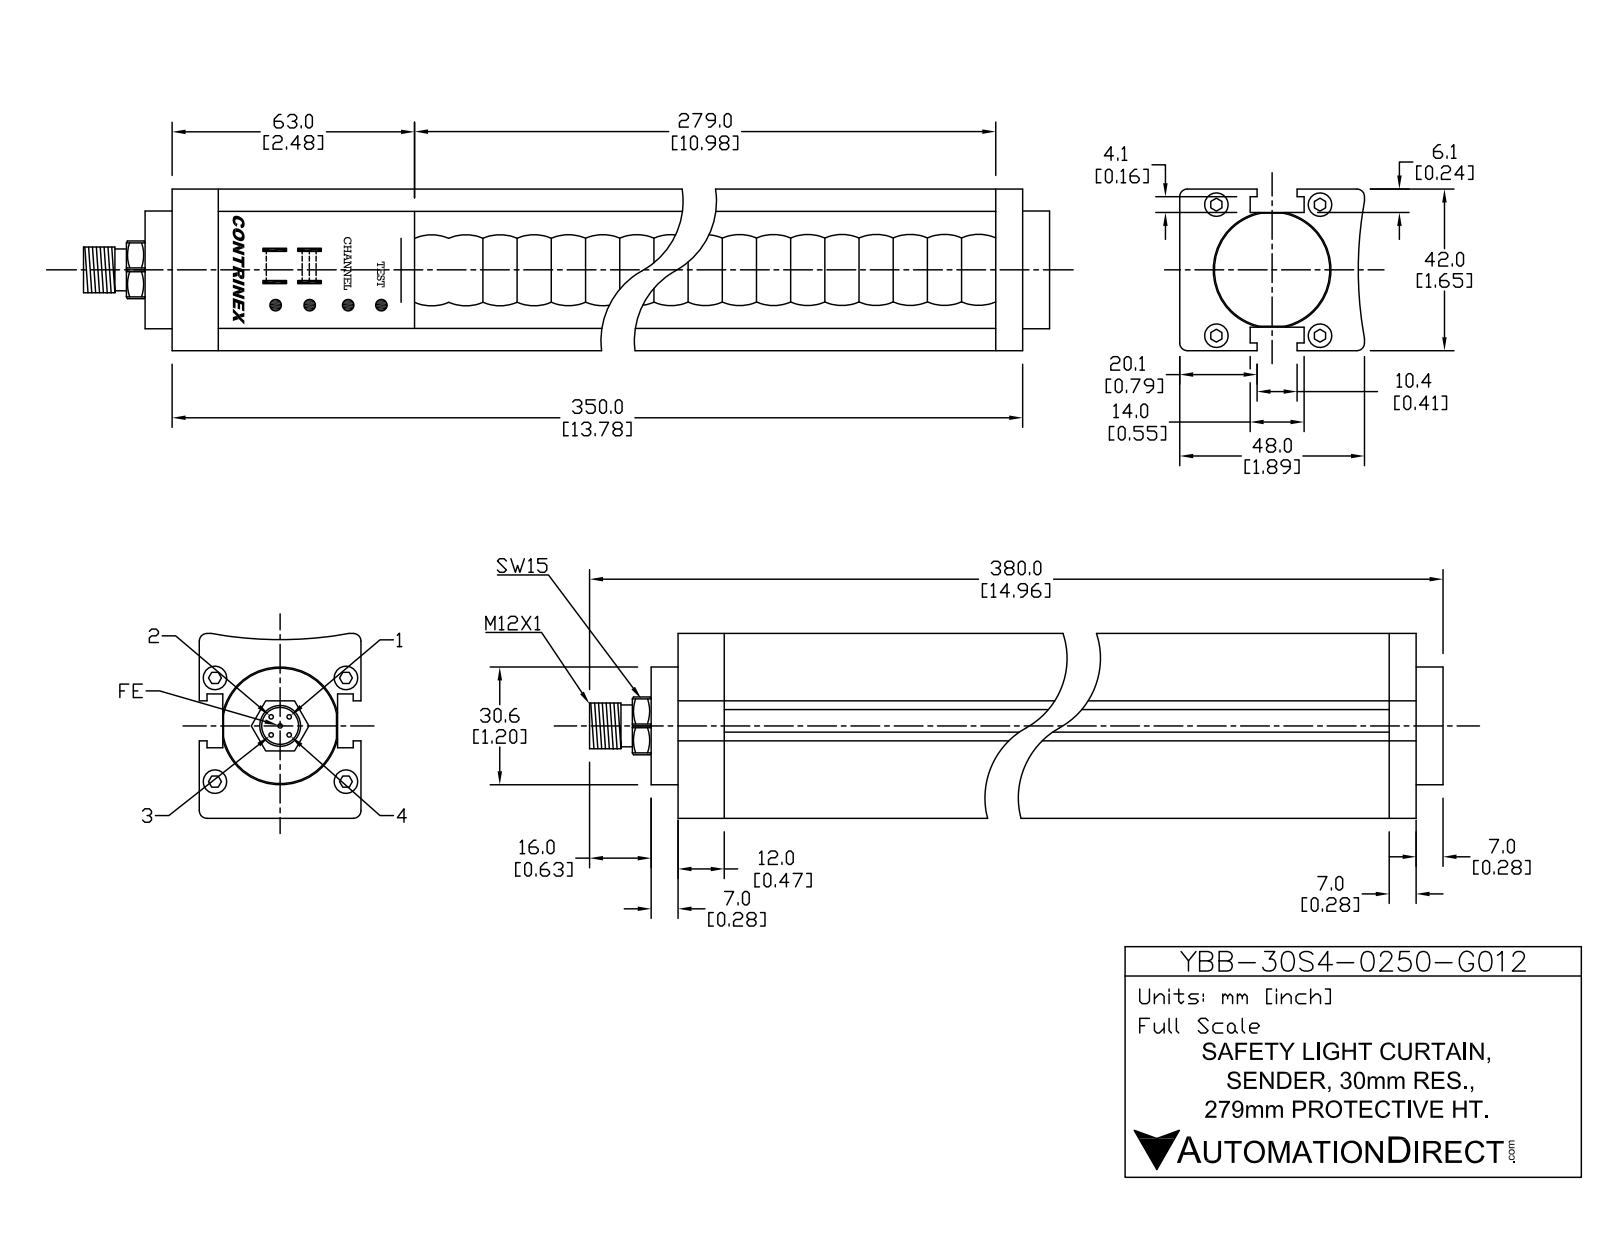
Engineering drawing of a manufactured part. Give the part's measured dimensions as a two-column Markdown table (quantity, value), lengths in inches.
| quantity | value |
| --- | --- |
| part name | YBB-30S4-0250-G012 |
| STEP written by | SolidWorks 2016 (AUTOMOTIVE_DESIGN) |
| units | inches |
| bodies | 19 solids, 440 faces (208 planar, 168 cylindrical, 64 other) |
| overall size | 14.961 × 1.89 × 1.654 |
| volume | 38.88 in³ |
| surface area | 143.3 in² |
| round holes (diameter × count) | 0.236 × 4, 0.335 × 1, 1.26 × 1 |
| round bosses / shafts (diameter × count) | 0.039 × 5, 0.217 × 4, 1.205 × 1, 0.472 × 1, 0.413 × 1 |
| partial cylindrical surfaces (radius × count) | 0.039 × 48, 0.02 × 4, 0.022 × 2, 0.323 × 1, 3.937 × 1 |
| main face-to-face distances | 0.248, 1.406, 1.654, 1.157, 12.992, 0.551, 0.677, 1.228, 0.315, 0.472 |
| hole center spacings | 0.828, 0.88, 1.059, 1.339, 1.707 |
